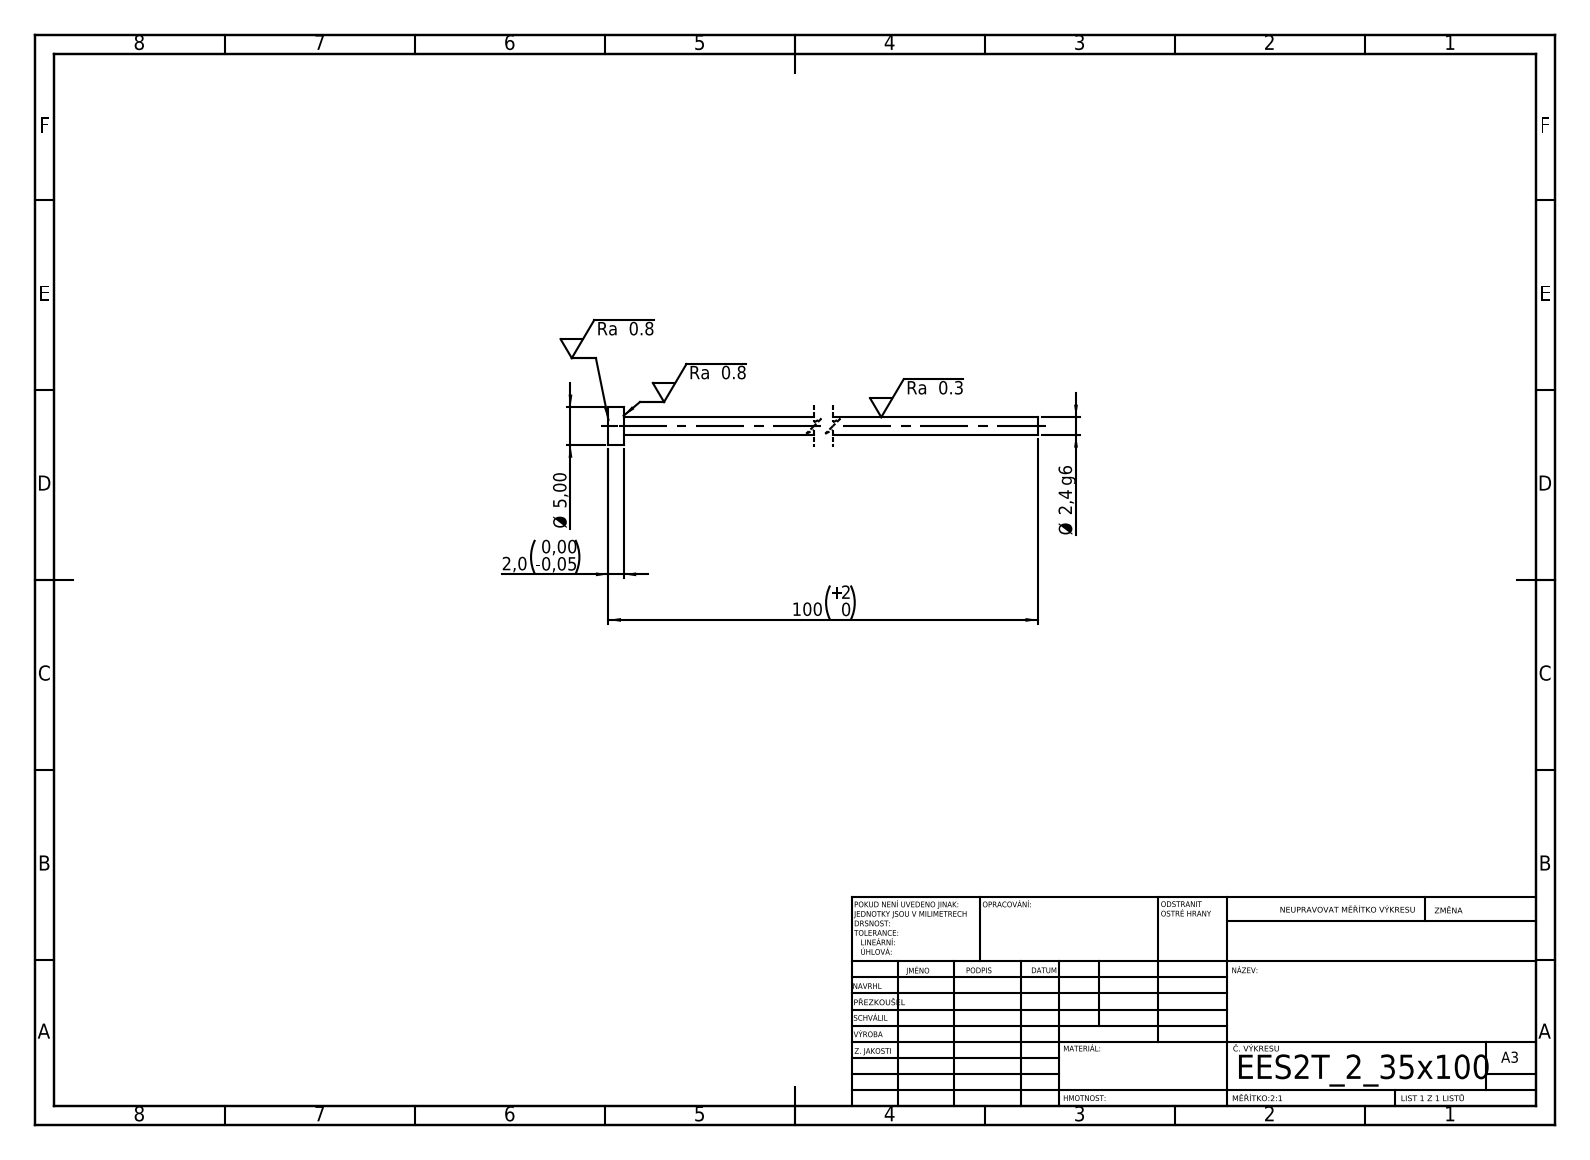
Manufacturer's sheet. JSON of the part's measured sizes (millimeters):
{"step_written_by": "SolidWorks 2019 (CONFIG_CONTROL_DESIGN)", "units": "millimeters", "bodies": {"solids": 1, "faces": 7, "planar": 3, "cylindrical": 4, "other": 0}, "overall_size": [100, 5, 5], "volume_mm3": 464, "surface_area_mm2": 794, "round_bosses_or_shafts": [[5, 1], [2.35, 1]], "face_to_face_distances": [2, 100, 98]}
